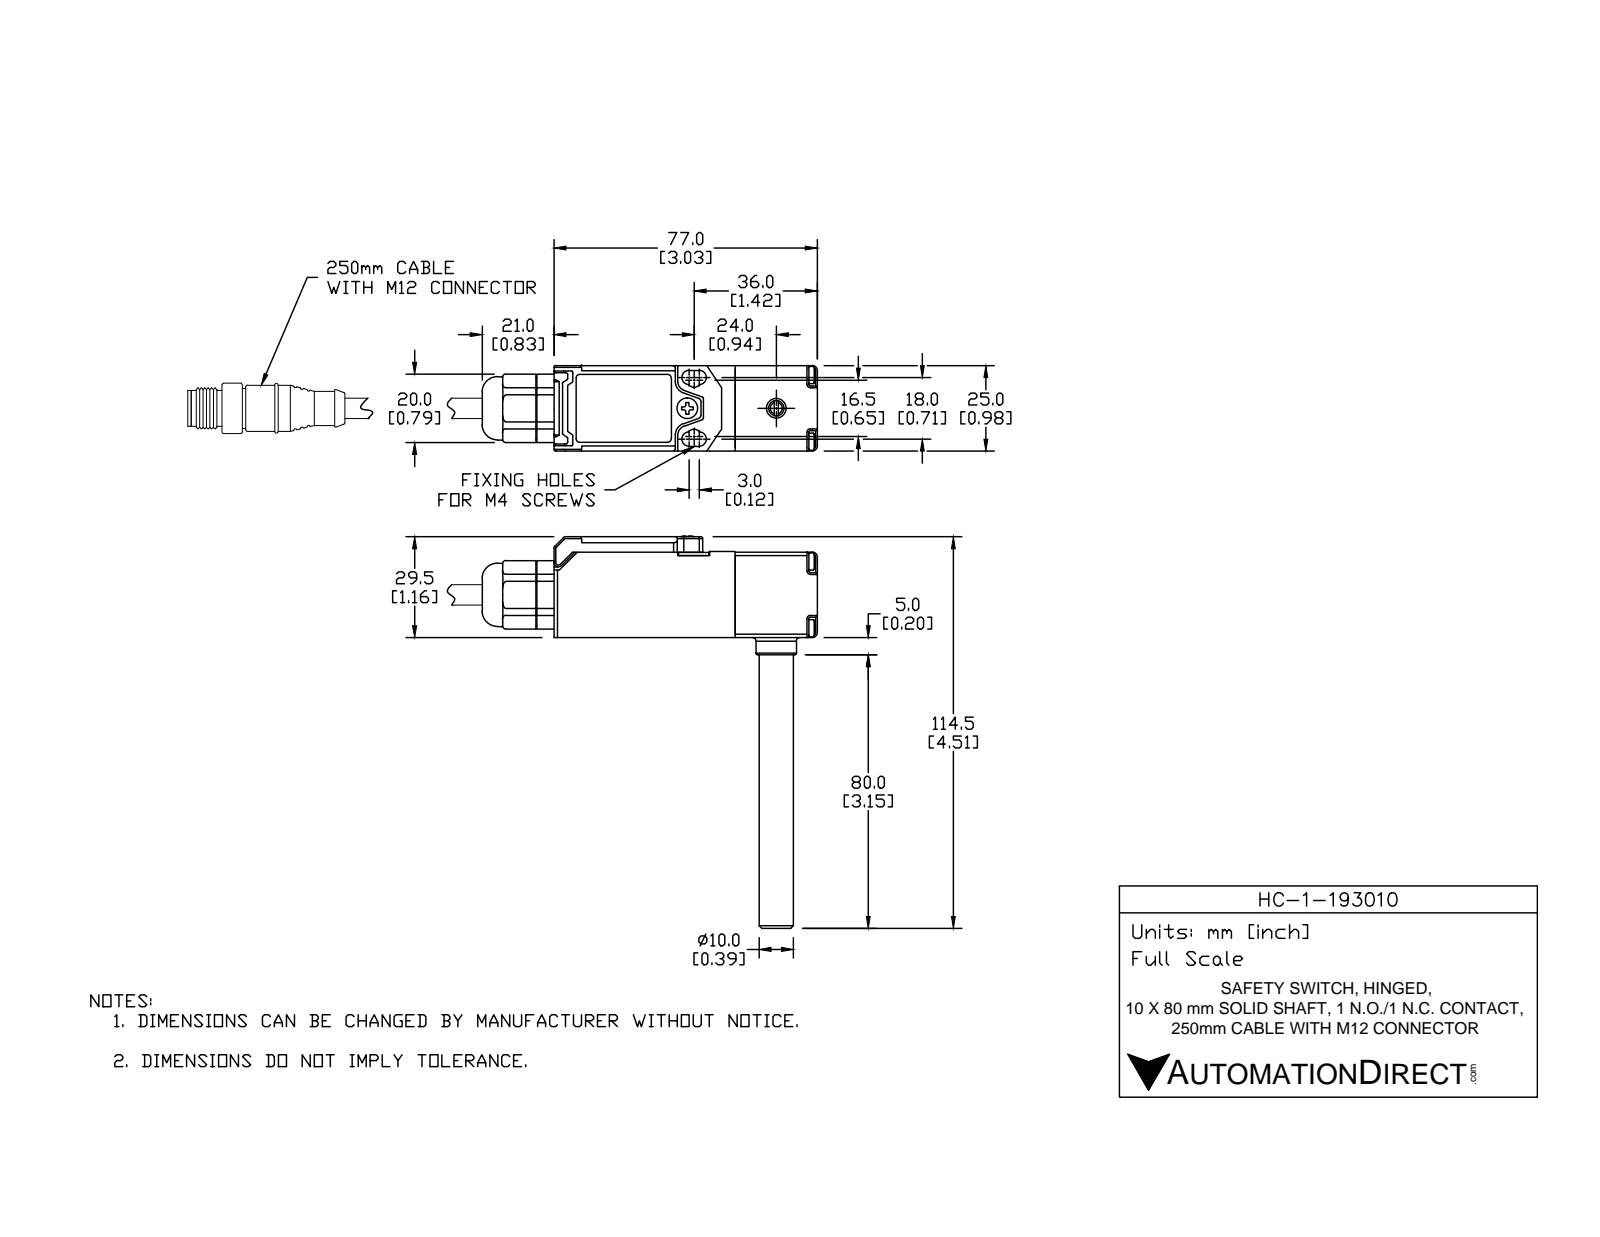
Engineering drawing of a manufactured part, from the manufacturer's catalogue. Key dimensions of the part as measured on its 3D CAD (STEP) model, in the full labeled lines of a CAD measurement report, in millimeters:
Part name (STEP PRODUCT): HC-1-193010
STEP written by: SolidWorks 2014 (AUTOMOTIVE_DESIGN)
Units: millimetres
Bodies: 14 solids, 1702 faces (700 planar, 601 cylindrical, 401 other)
Overall size (bounding box): 114.7 × 80.5 × 25
Volume: 31 660 mm³ · Surface area: 28 710 mm²
Round holes (diameter × count): ⌀3.2 ×5, ⌀2.4 ×4, ⌀1.5 ×2, ⌀1.6 ×2, ⌀1.8 ×2, ⌀2.2 ×2, ⌀3.6 ×2, ⌀1.4 ×1, ⌀2.1 ×1, ⌀2.5 ×1, ⌀2.6 ×1, ⌀4.7 ×1
Round bosses / shafts (diameter × count): ⌀2.6 ×5, ⌀5 ×4, ⌀2 ×4, ⌀3.5 ×2, ⌀18.8 ×1, ⌀13.5 ×1, ⌀10 ×1, ⌀9.8 ×1
Partial cylindrical surfaces — rounded edges, fillets, slot ends (radius × count): R0.5 ×226, R0.1 ×24, R0.3 ×20, R1 ×20, R1.5 ×7, R2.1 ×6, R2.8 ×6, R0.2 ×4
Main face-to-face distances: 25, 2, 1.8, 23.2, 1, 23, 24, 21, 22.2, 29.2
Hole centre spacings: 13.8, 19.5, 4.3, 4.7, 6.2, 10.5, 10.7, 10.8
